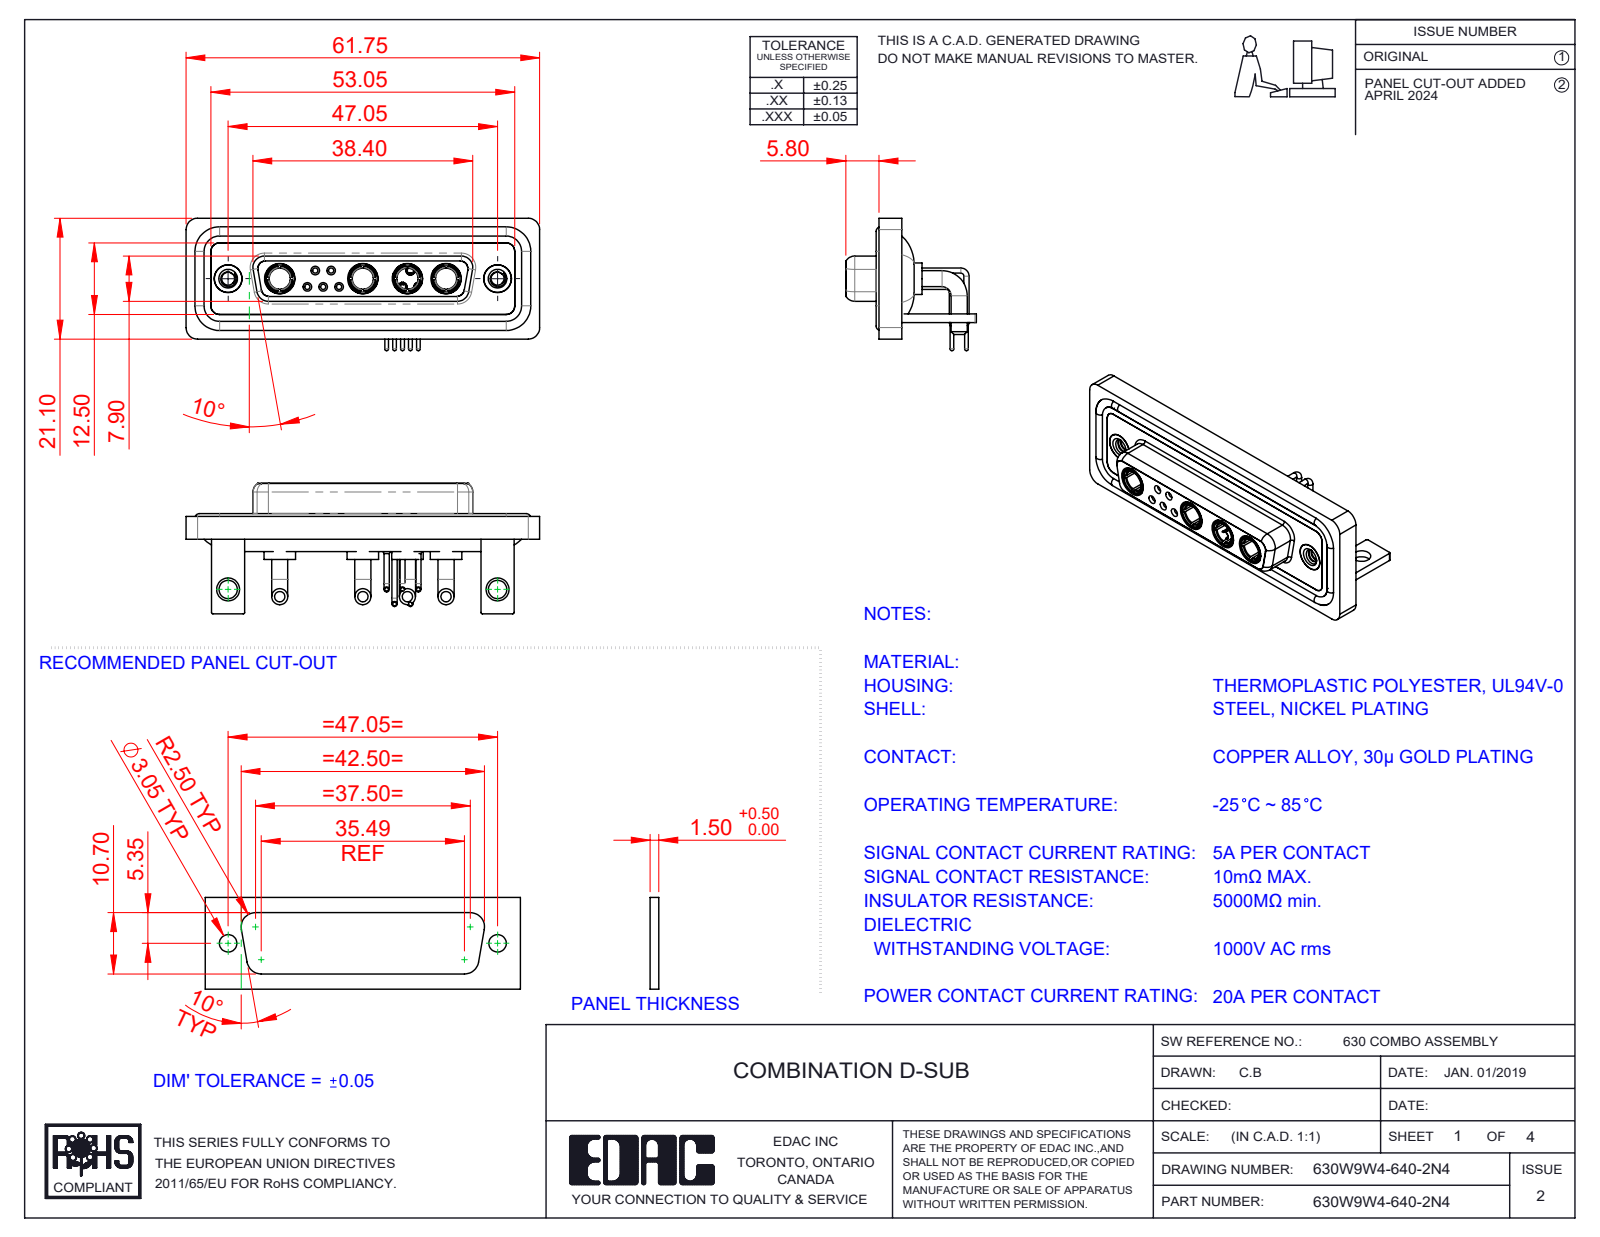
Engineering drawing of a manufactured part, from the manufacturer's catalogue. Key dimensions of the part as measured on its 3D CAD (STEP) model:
Part name (STEP PRODUCT): 630Combo Shell Rear_25 Contacts; Power Socket_20A RA; 630Combo Shell Front_25 Contacts; 630Combo Housing_9W4 (+6 more)
STEP written by: SolidWorks 2023 (CONFIG_CONTROL_DESIGN)
Units: millimetres
Bodies: 22 solids, 1011 faces (316 planar, 427 cylindrical, 268 other)
Overall size (bounding box): 61.75 × 23.12 × 22.8
Volume: 8 818 mm³ · Surface area: 14 782 mm²
Round holes (diameter × count): ⌀4.85 ×6, ⌀0.9 ×5, ⌀1.1 ×5, ⌀1.5 ×5, ⌀2 ×5, ⌀3.7 ×4, ⌀5.3 ×4, ⌀1.6 ×3, ⌀1.7 ×2, ⌀2.26 ×2, ⌀3.2 ×2, ⌀4 ×2
Round bosses / shafts (diameter × count): ⌀0.9 ×10, ⌀1.6 ×9, ⌀2.8 ×8, ⌀2 ×5, ⌀1.5 ×5, ⌀0.65 ×5, ⌀5.5 ×4, ⌀5.2 ×4
Partial cylindrical surfaces — rounded edges, fillets, slot ends (radius × count): R2 ×19, R1.5 ×18, R0.25 ×16, R1.35 ×8, R1.6 ×8, R0.5 ×5, R0.6 ×4, R0.65 ×4
Main face-to-face distances: 0.4, 1.8, 2.9, 3.7, 1.5, 4.1, 1.1, 1.4, 1.6, 2.5
Hole centre spacings: 3.16, 2.77, 5.04, 13.85, 11.08, 12.79, 15.5, 5.54
